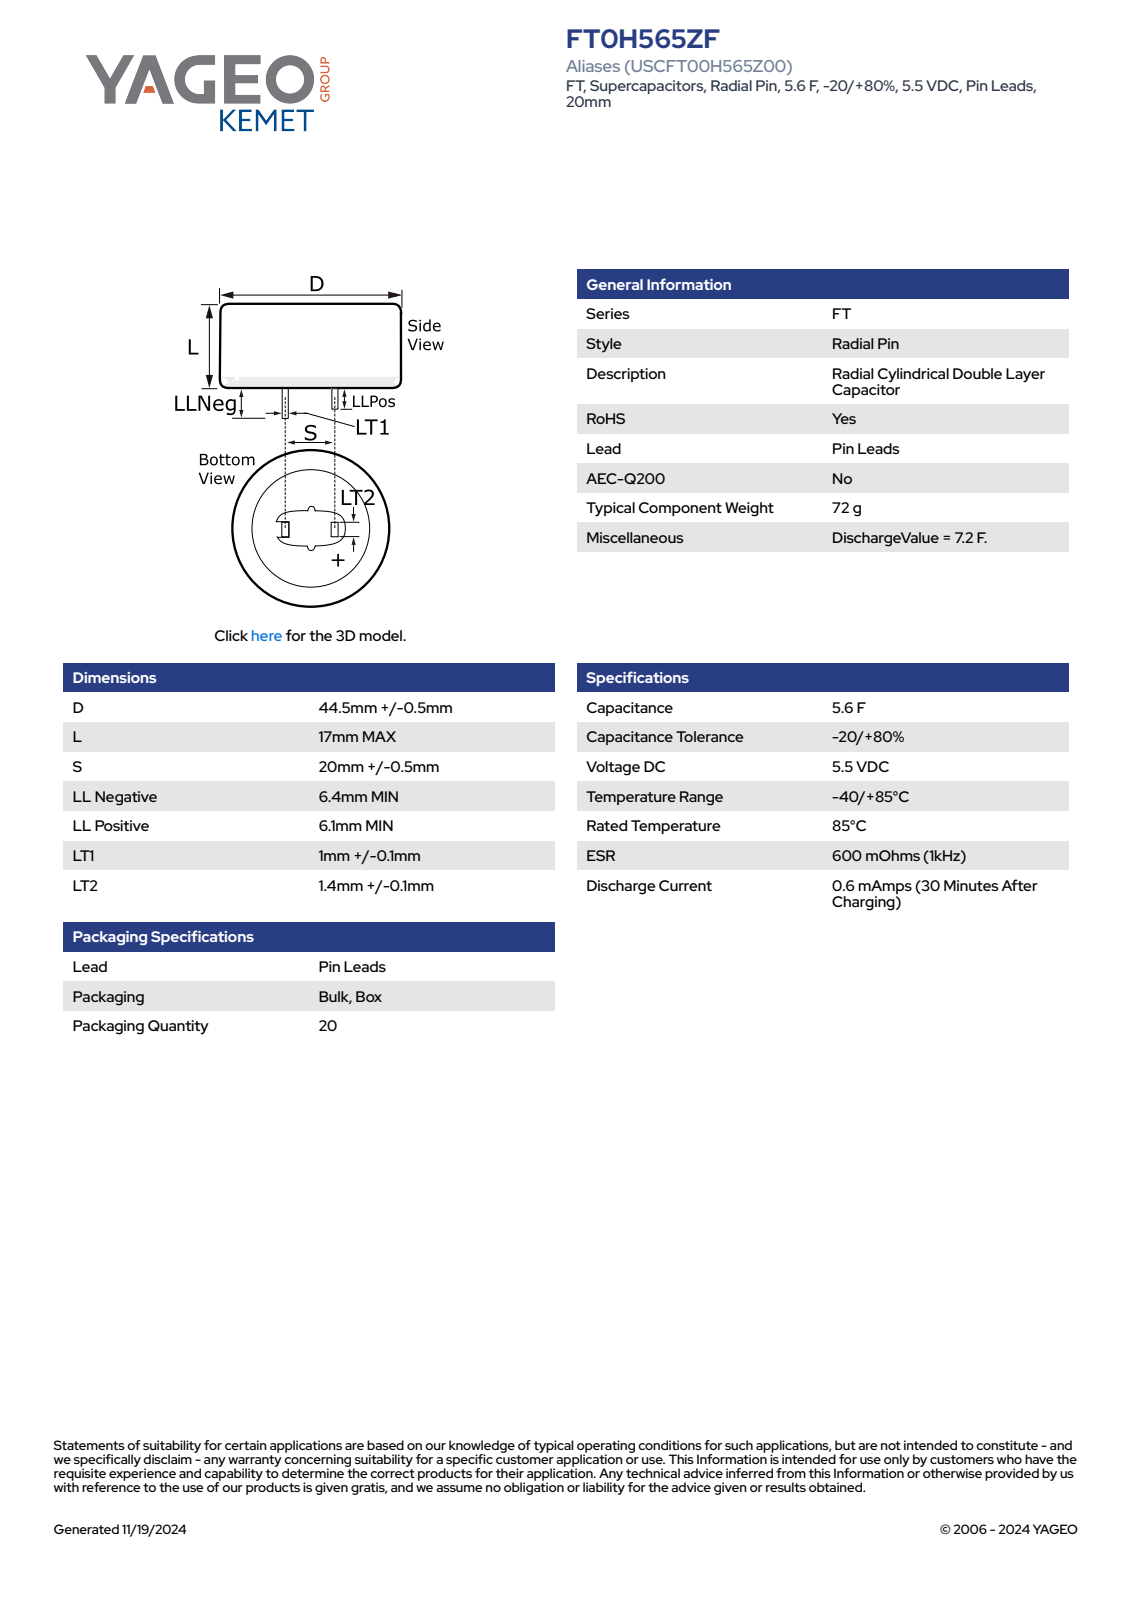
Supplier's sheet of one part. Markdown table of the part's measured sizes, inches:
| quantity | value |
| --- | --- |
| part name | CDR_LPLLN_D45L17S20LLNEG6.4LLPOS6.1LT11.1LT21.5 |
| STEP written by | SolidWorks 2014 (AUTOMOTIVE_DESIGN) |
| units | inches |
| bodies | 1 solid, 78 faces (70 planar, 4 cylindrical, 4 other) |
| overall size | 1.772 × 1.772 × 0.921 |
| volume | 1.647 in³ |
| surface area | 8.55 in² |
| round bosses / shafts (diameter × count) | 1.772 × 1 |
| partial cylindrical surfaces (radius × count) | 0.886 × 1 |
| main face-to-face distances | 0.669, 0.043, 0.787, 0.059, 0.831, 0.744, 0.252, 0.921, 0.24, 0.909 |
